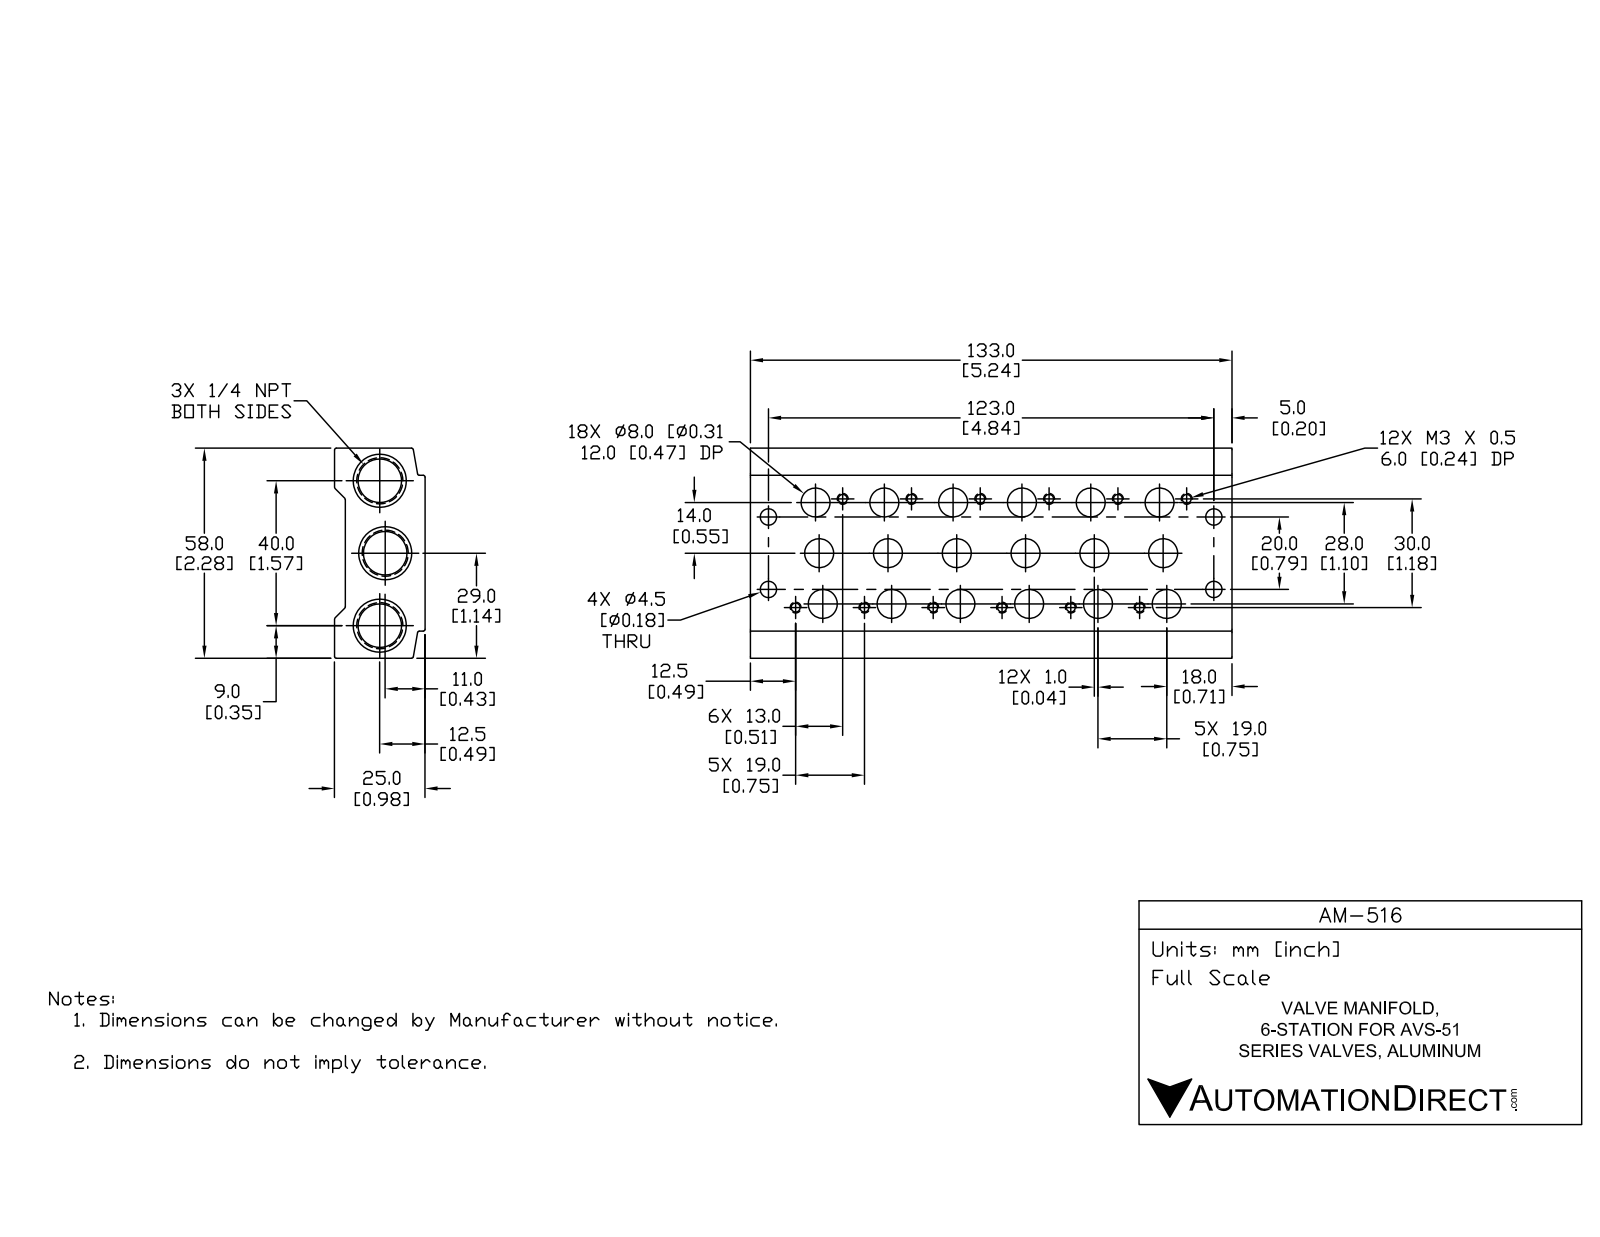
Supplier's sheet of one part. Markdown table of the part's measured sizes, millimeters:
| quantity | value |
| --- | --- |
| part name | AM-516 |
| STEP written by | SolidWorks 2015 (CONFIG_CONTROL_DESIGN) |
| units | millimeters |
| bodies | 1 solid, 153 faces (32 planar, 85 cylindrical, 36 other) |
| overall size | 133 × 58 × 25 |
| volume | 124 812 mm³ |
| surface area | 42 211 mm² |
| round holes (diameter × count) | 2.5 × 12, 6.5 × 12, 10.2 × 6, 4.5 × 4, 11.13 × 3 |
| partial cylindrical surfaces (radius × count) | 0.5 × 11 |
| main face-to-face distances | 22, 58, 3, 25, 133, 6, 52, 15, 12, 10 |
| hole center spacings | 19, 38, 57, 7.57, 14.04, 16.35, 29.52, 76 |
